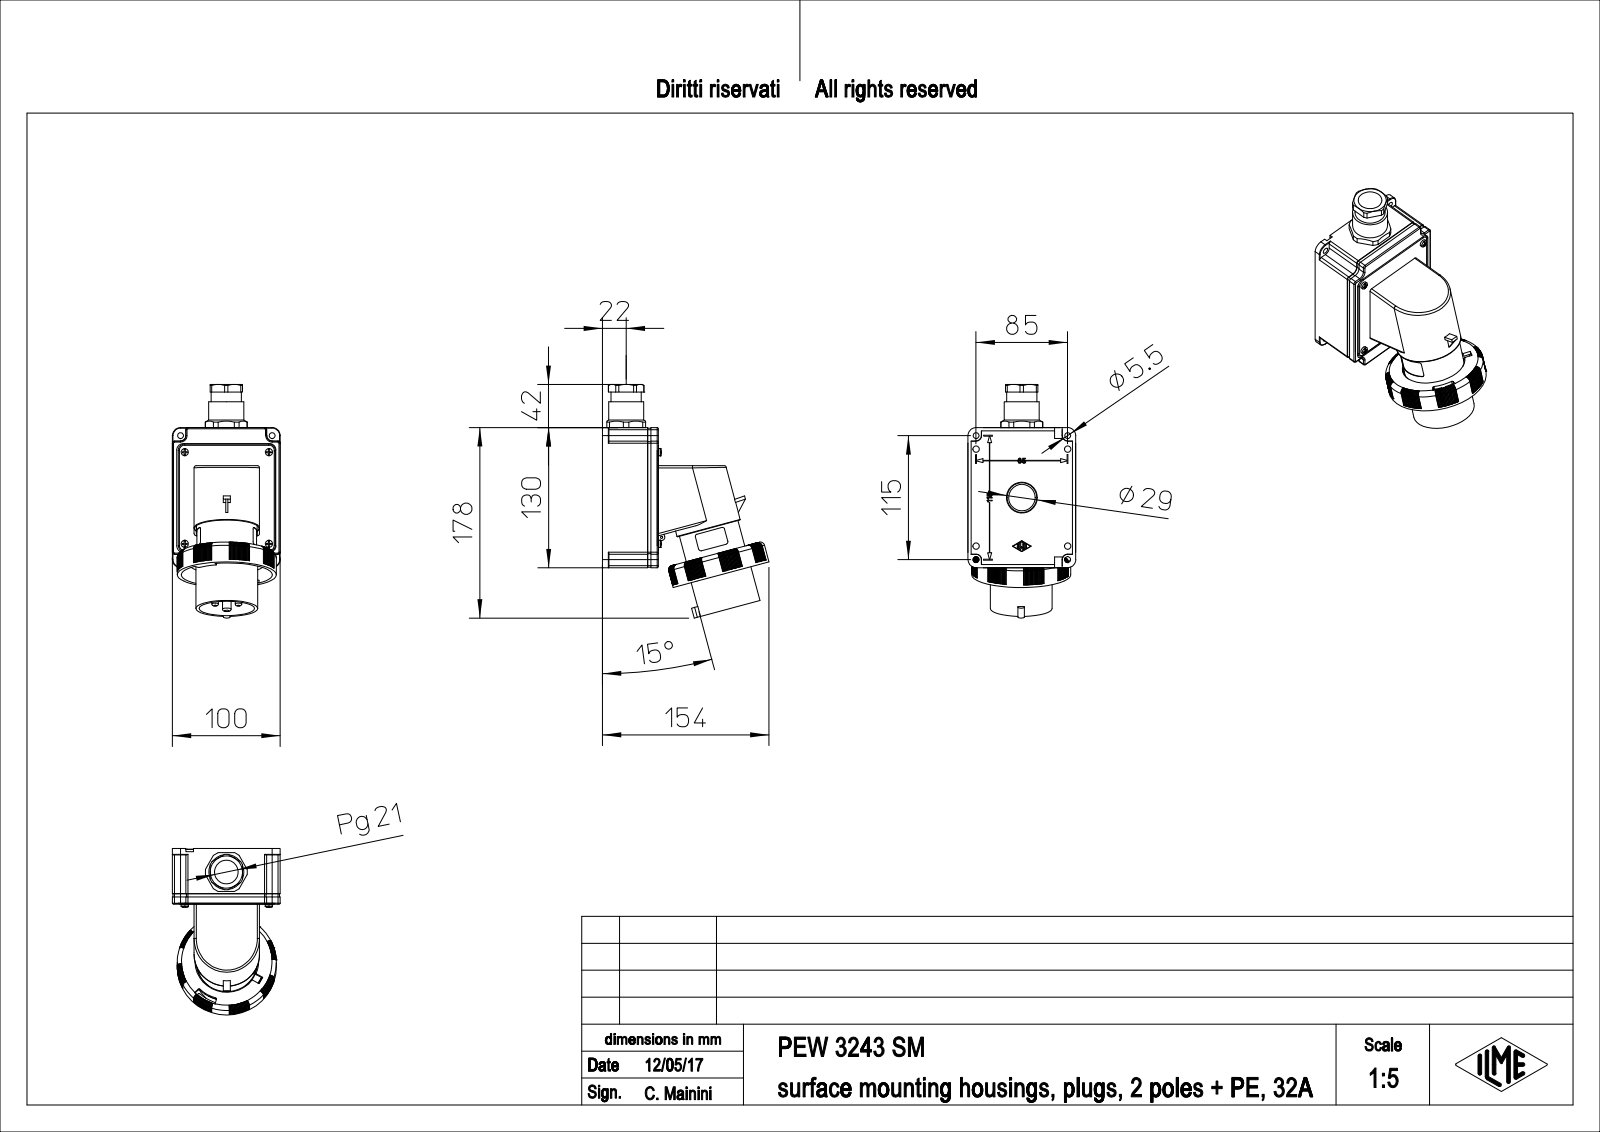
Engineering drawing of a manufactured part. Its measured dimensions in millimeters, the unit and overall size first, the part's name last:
Units: millimetres
Overall size (bounding box): 216.68 × 154.57 × 100
Round holes (diameter × count): ⌀5.5 ×8, ⌀6 ×4, ⌀4 ×2, ⌀4.2 ×2, ⌀6.1 ×2, ⌀28.6 ×2, ⌀2 ×1, ⌀22 ×1, ⌀84.5 ×1
Round bosses / shafts (diameter × count): ⌀6.7 ×6, ⌀6 ×2, ⌀3 ×2, ⌀92 ×1, ⌀70 ×1, ⌀60.7 ×1, ⌀57.3 ×1, ⌀56.2 ×1
Partial cylindrical surfaces — rounded edges, fillets, slot ends (radius × count): R3.6 ×136, R0.5 ×18, R1 ×10, R2 ×10, R41.53 ×10, R1.5 ×8, R6 ×8, R0.3 ×4
Main face-to-face distances: 2, 4.5, 44.3, 50.8, 6.5, 46.3, 3, 100, 94.65, 6.85
Hole centre spacings: 12.5, 85, 61.9, 71.5, 85.91, 102.5, 133.16, 21
Volume: 971 882 mm³ · Surface area: 156 731 mm²
Bodies: 1 solid, 1809 faces (910 planar, 379 cylindrical, 520 other)
Part name (STEP PRODUCT): PEW_3243_SM
STEP written by: PTC Creo Elements/Direct Modeling 19.0E 27-Jun-2016 (C) Parametric Technology GmbH (AUTOMOTIVE_DESIGN)
